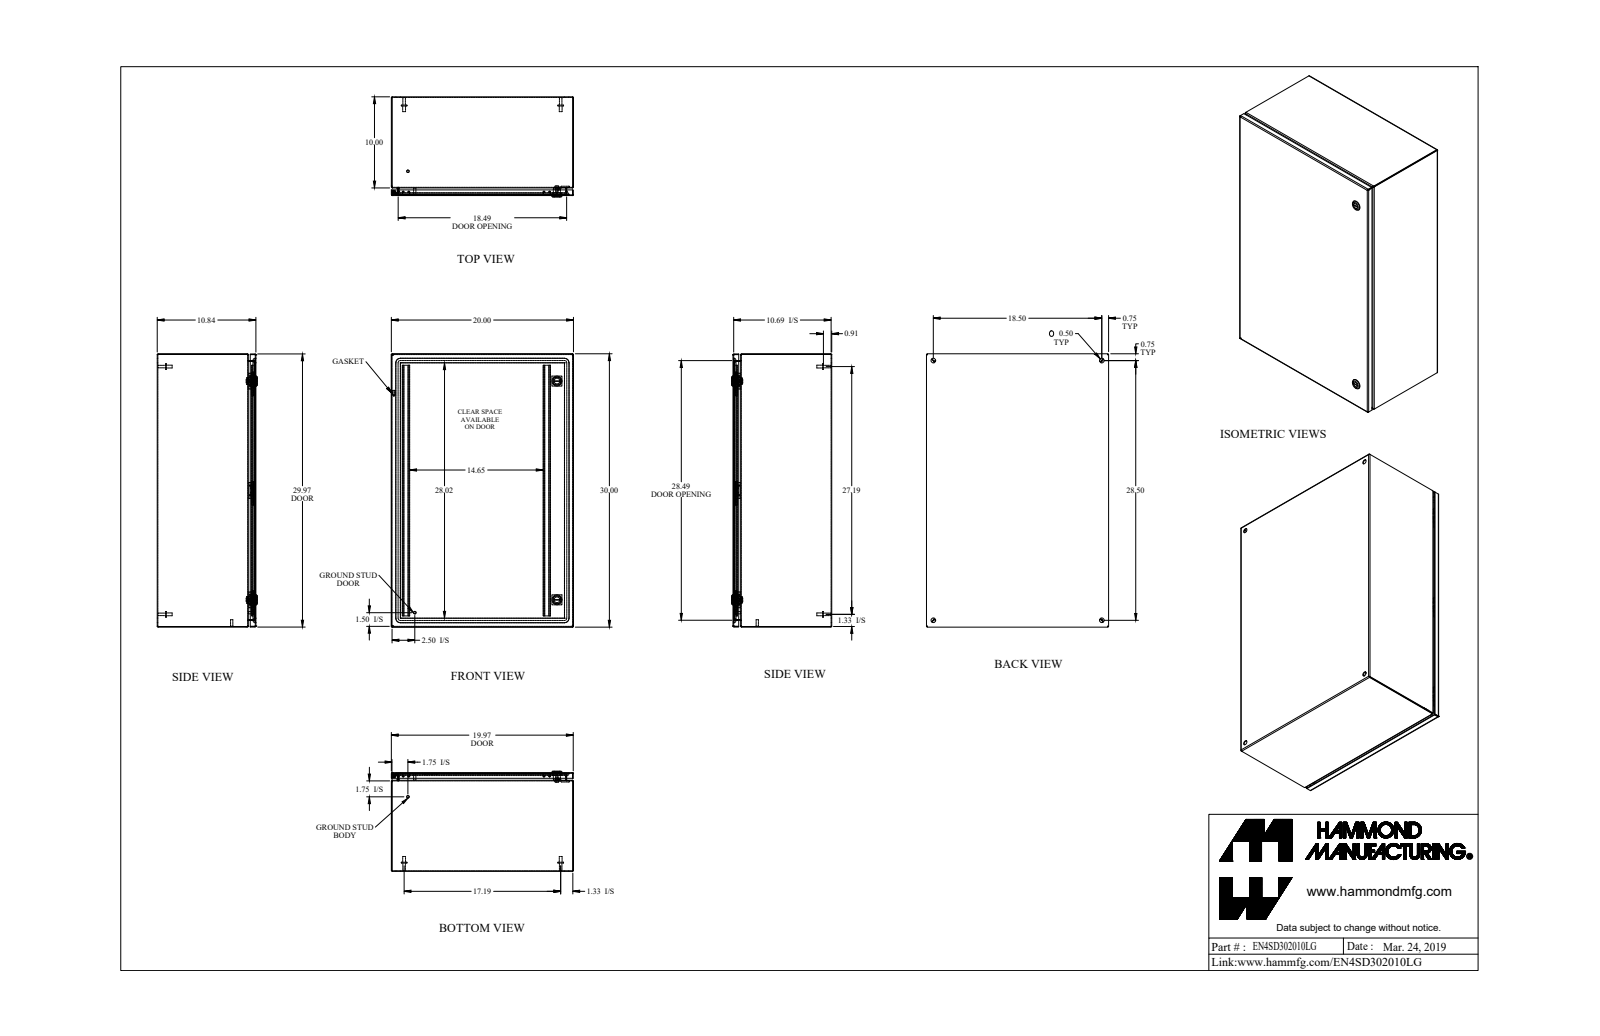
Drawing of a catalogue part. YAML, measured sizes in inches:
part_name: "EN4SD302010LG"
step_written_by: "SolidWorks 2019 (AUTOMOTIVE_DESIGN)"
units: inches
bodies: {solids: 31, faces: 854, planar: 395, cylindrical: 295, other: 164}
overall_size: [30, 20, 10.997]
volume: 186.1
surface_area: 5229
round_holes:
  - {diameter: 0.5, count: 4}
  - {diameter: 0.232, count: 2}
  - {diameter: 0.625, count: 2}
  - {diameter: 0.785, count: 2}
  - {diameter: 0.172, count: 1}
  - {diameter: 0.24, count: 1}
  - {diameter: 0.242, count: 1}
round_bosses_or_shafts:
  - {diameter: 0.625, count: 4}
  - {diameter: 0.313, count: 4}
  - {diameter: 0.27, count: 4}
  - {diameter: 1.1, count: 2}
  - {diameter: 0.525, count: 2}
  - {diameter: 0.281, count: 2}
  - {diameter: 0.25, count: 2}
  - {diameter: 0.455, count: 1}
partial_cylinders:
  - {radius: 0.036, count: 16}
  - {radius: 0.108, count: 16}
  - {radius: 0.043, count: 12}
  - {radius: 0.081, count: 12}
  - {radius: 0.382, count: 12}
  - {radius: 0.1, count: 8}
  - {radius: 19.003, count: 8}
  - {radius: 0.006, count: 6}
face_to_face_distances: [0.072, 10.765, 10.693, 10.837, 19.928, 29.928, 19.856, 20, 29.856, 30]
hole_center_spacings: [18.5, 28.5, 33.978, 2.493, 2.494, 17.572, 17.572, 23.999]
